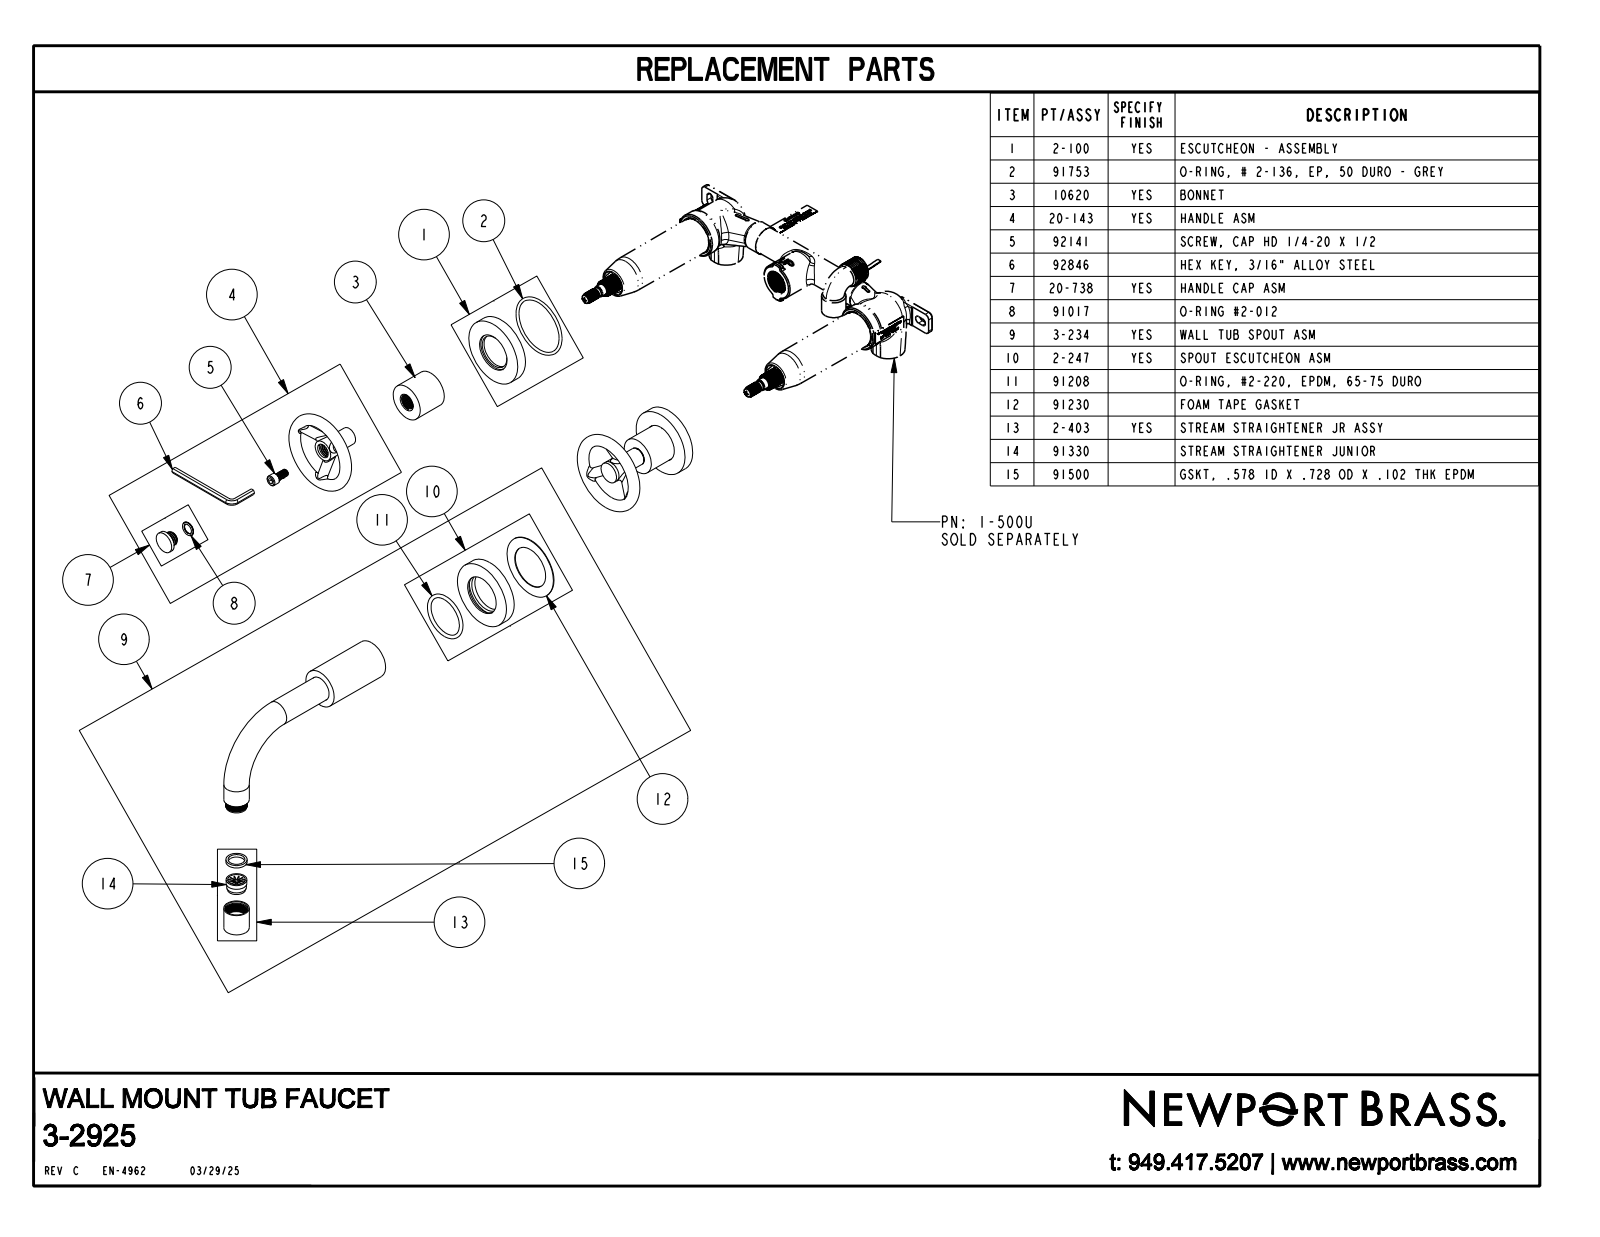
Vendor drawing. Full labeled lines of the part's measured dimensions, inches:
Part name (STEP PRODUCT): 3-2925_SW0001
STEP written by: CREO PARAMETRIC BY PTC INC, 2018400 (AUTOMOTIVE_DESIGN)
Units: inches
Bodies: 3 solids, 96 faces (14 planar, 36 cylindrical, 46 other)
Overall size (bounding box): 10.878 × 10.75 × 5.998
Volume: 17.18 in³ · Surface area: 97.51 in²
Round bosses / shafts (diameter × count): ⌀0.35 ×6, ⌀2.375 ×3, ⌀1.313 ×2, ⌀0.875 ×2, ⌀0.75 ×2, ⌀0.63 ×2, ⌀1.375 ×1
Main face-to-face distances: 0.375, 1.483, 1.108, 1.5, 2.893, 1.125, 2.518, 0.017, 1.41, 1.393
